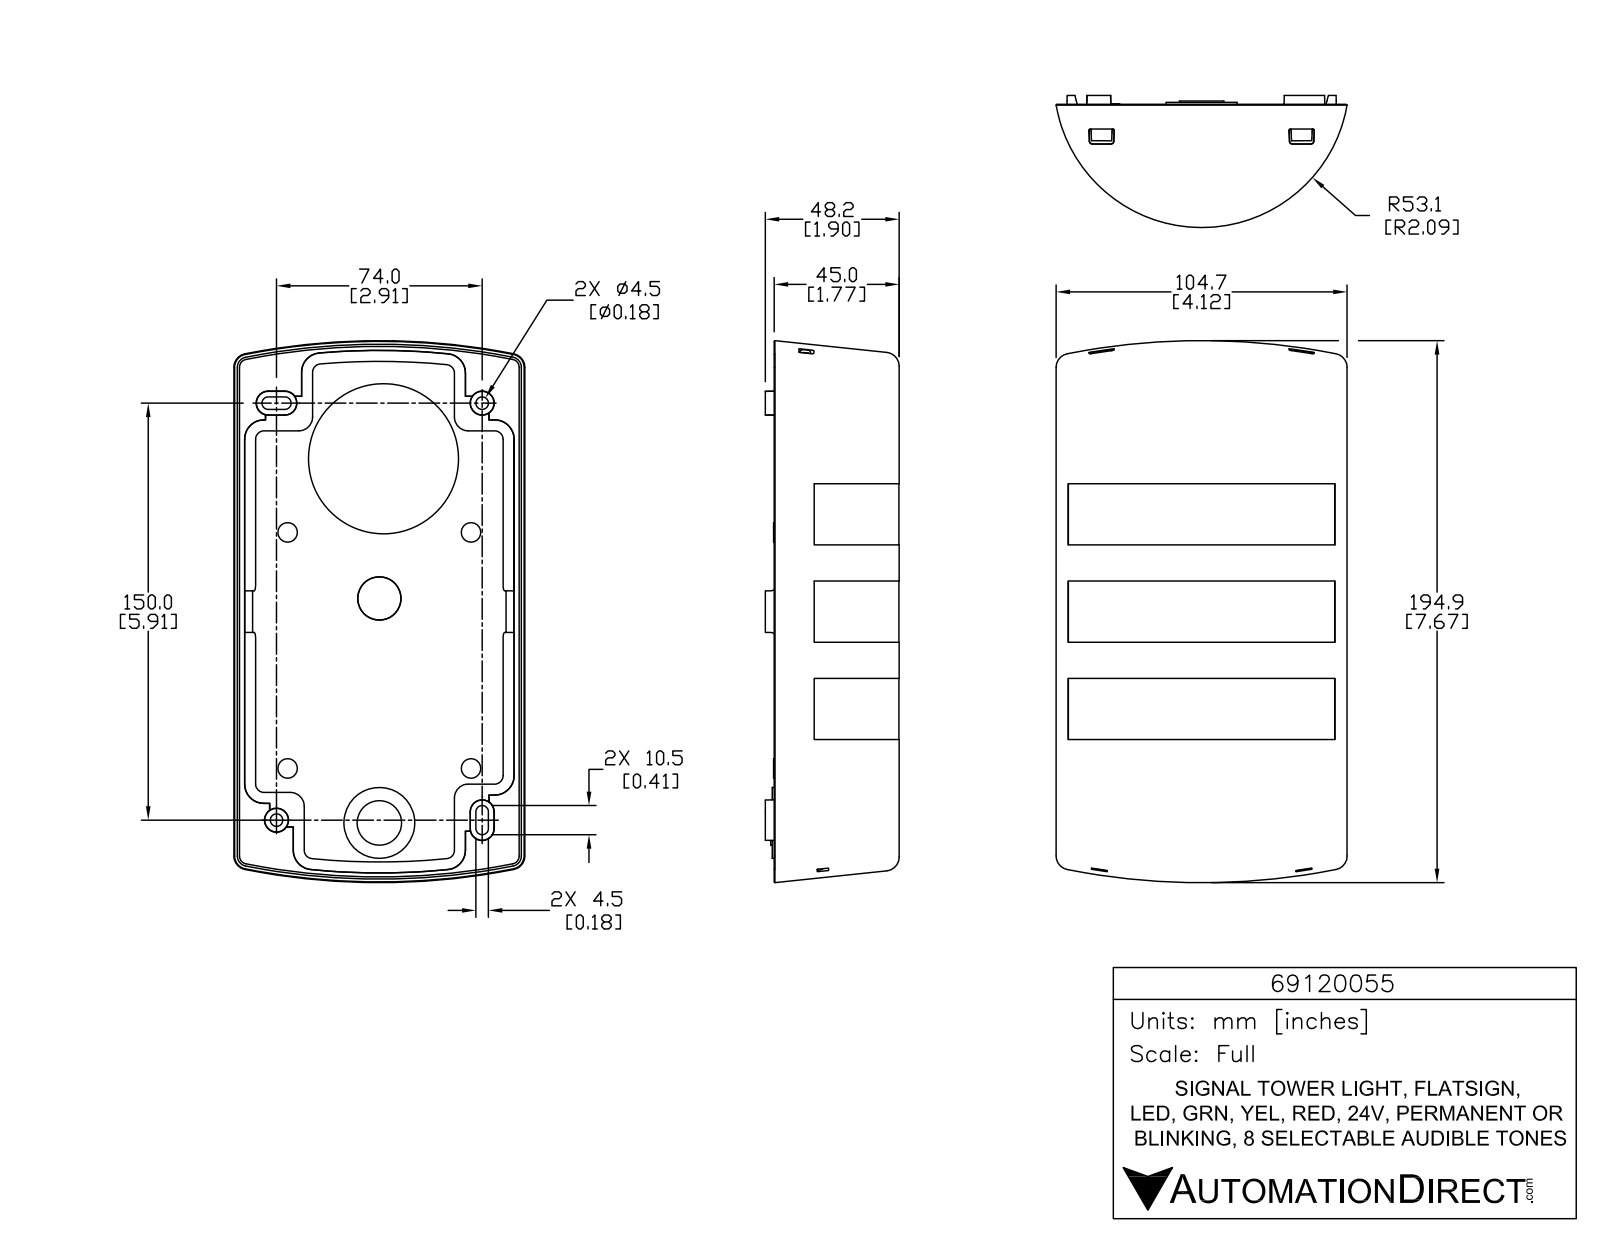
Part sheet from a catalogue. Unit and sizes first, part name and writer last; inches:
Units: inches
Overall size (bounding box): 7.675 × 4.122 × 1.901
Round holes (diameter × count): ⌀0.089 ×1
Round bosses / shafts (diameter × count): ⌀2.126 ×1, ⌀1.004 ×1, ⌀0.63 ×1, ⌀0.514 ×1, ⌀0.128 ×1
Partial cylindrical surfaces — rounded edges, fillets, slot ends (radius × count): R0.039 ×12, R0.012 ×4, R0.008 ×3, R0.008 ×2, R0.018 ×2, R0.019 ×2, R0.019 ×2, R0.02 ×2
Main face-to-face distances: 0.031, 0.079, 0.047, 0.11, 0.063, 0.157, 0.039, 0.02, 0.138, 0.118
Volume: 38.36 in³ · Surface area: 92.68 in²
Bodies: 1 solid, 1074 faces (520 planar, 128 cylindrical, 426 other)
Part name (STEP PRODUCT): 69120055
STEP written by: SolidWorks 2017 (AUTOMOTIVE_DESIGN)
